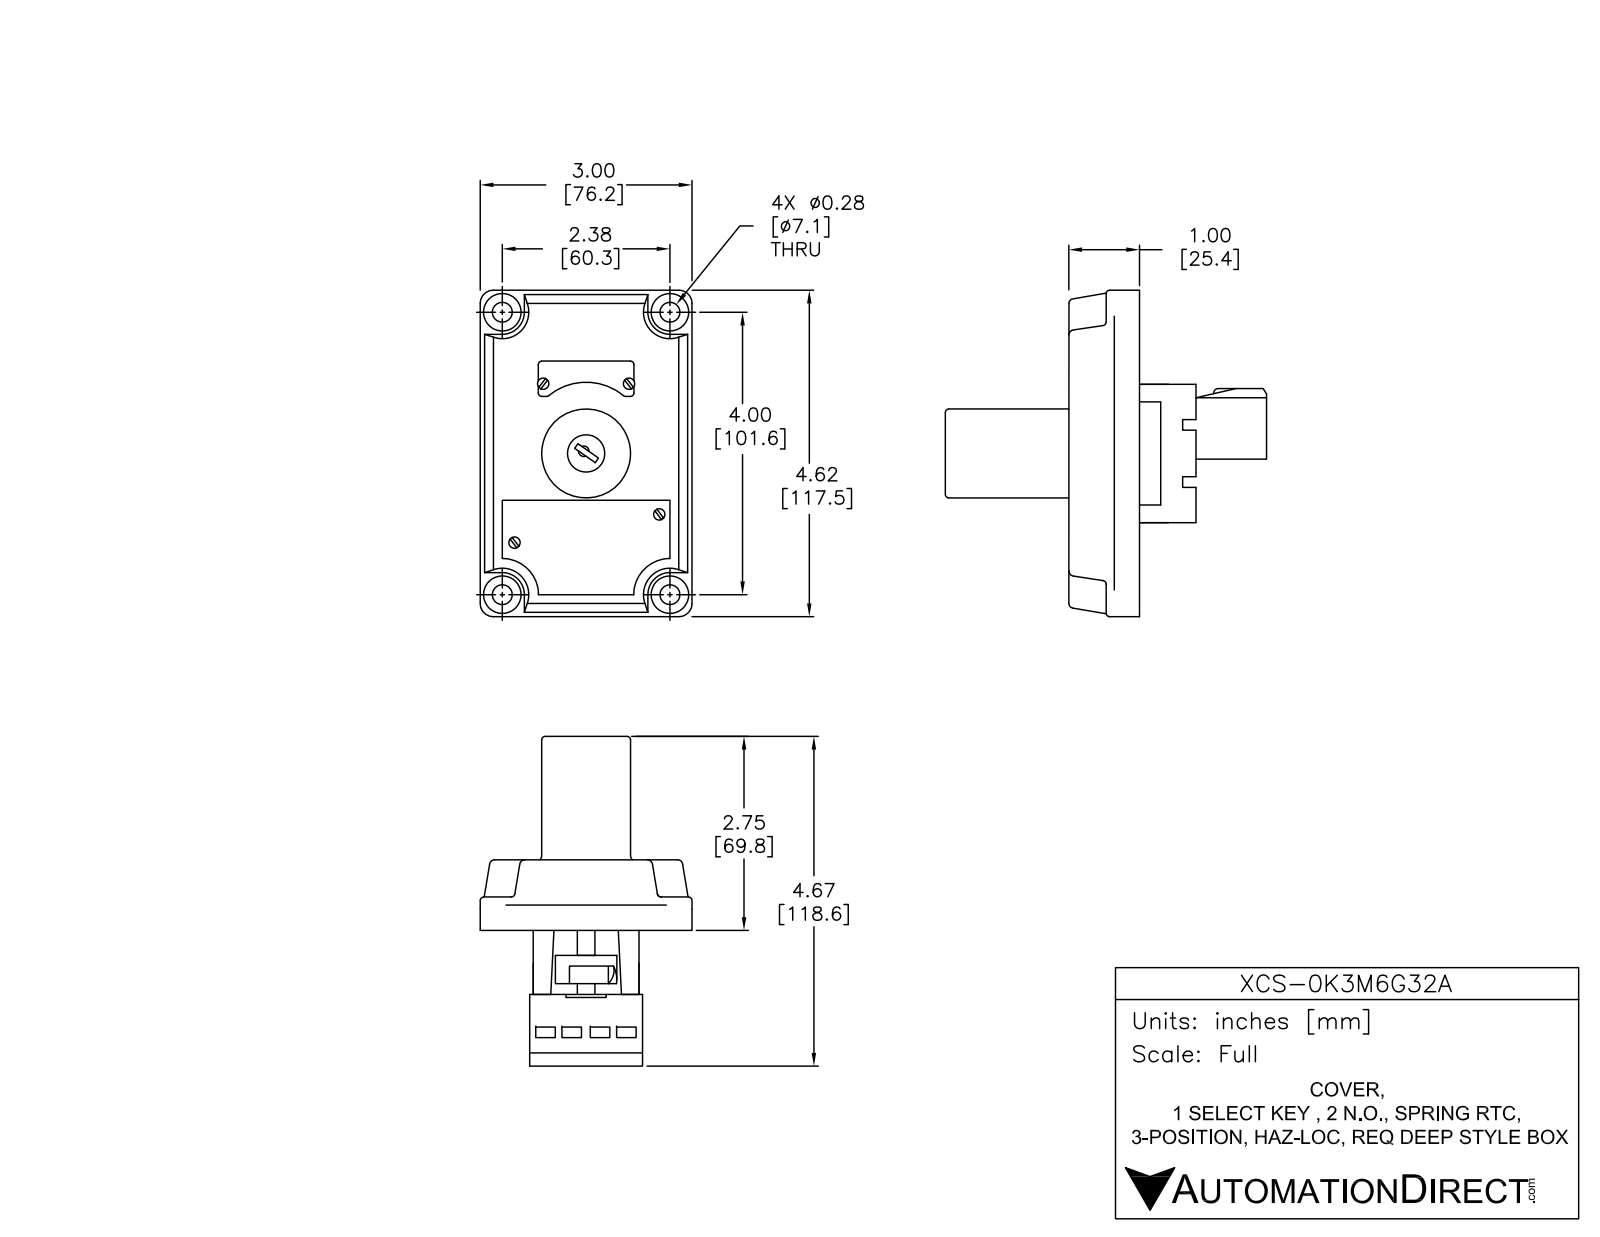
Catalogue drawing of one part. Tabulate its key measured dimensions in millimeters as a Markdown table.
| quantity | value |
| --- | --- |
| part name | XCS-0K3M6G32A |
| STEP written by | SolidWorks 2015 (AUTOMOTIVE_DESIGN) |
| units | millimeters |
| bodies | 10 solids, 476 faces (177 planar, 169 cylindrical, 130 other) |
| overall size | 117.6 × 106.46 × 78.74 |
| volume | 229 688 mm³ |
| surface area | 58 343 mm² |
| round holes (diameter × count) | 6.65 × 4, 6.86 × 4, 13.41 × 1 |
| round bosses / shafts (diameter × count) | 3.3 × 6, 11.6 × 4, 6.35 × 4, 32 × 1 |
| partial cylindrical surfaces (radius × count) | 0.25 × 28, 1.27 × 10, 0.51 × 8, 1.4 × 8, 3 × 8, 2.38 × 4, 2.54 × 4, 9.65 × 4 |
| main face-to-face distances | 13.34, 12.7, 26.04, 11.3, 24, 37.34, 17.5, 6.5, 4.8, 30.84 |
| hole center spacings | 59.11, 10.2, 20.4, 60.46, 101.6, 118.23, 10.13, 10.18 |
